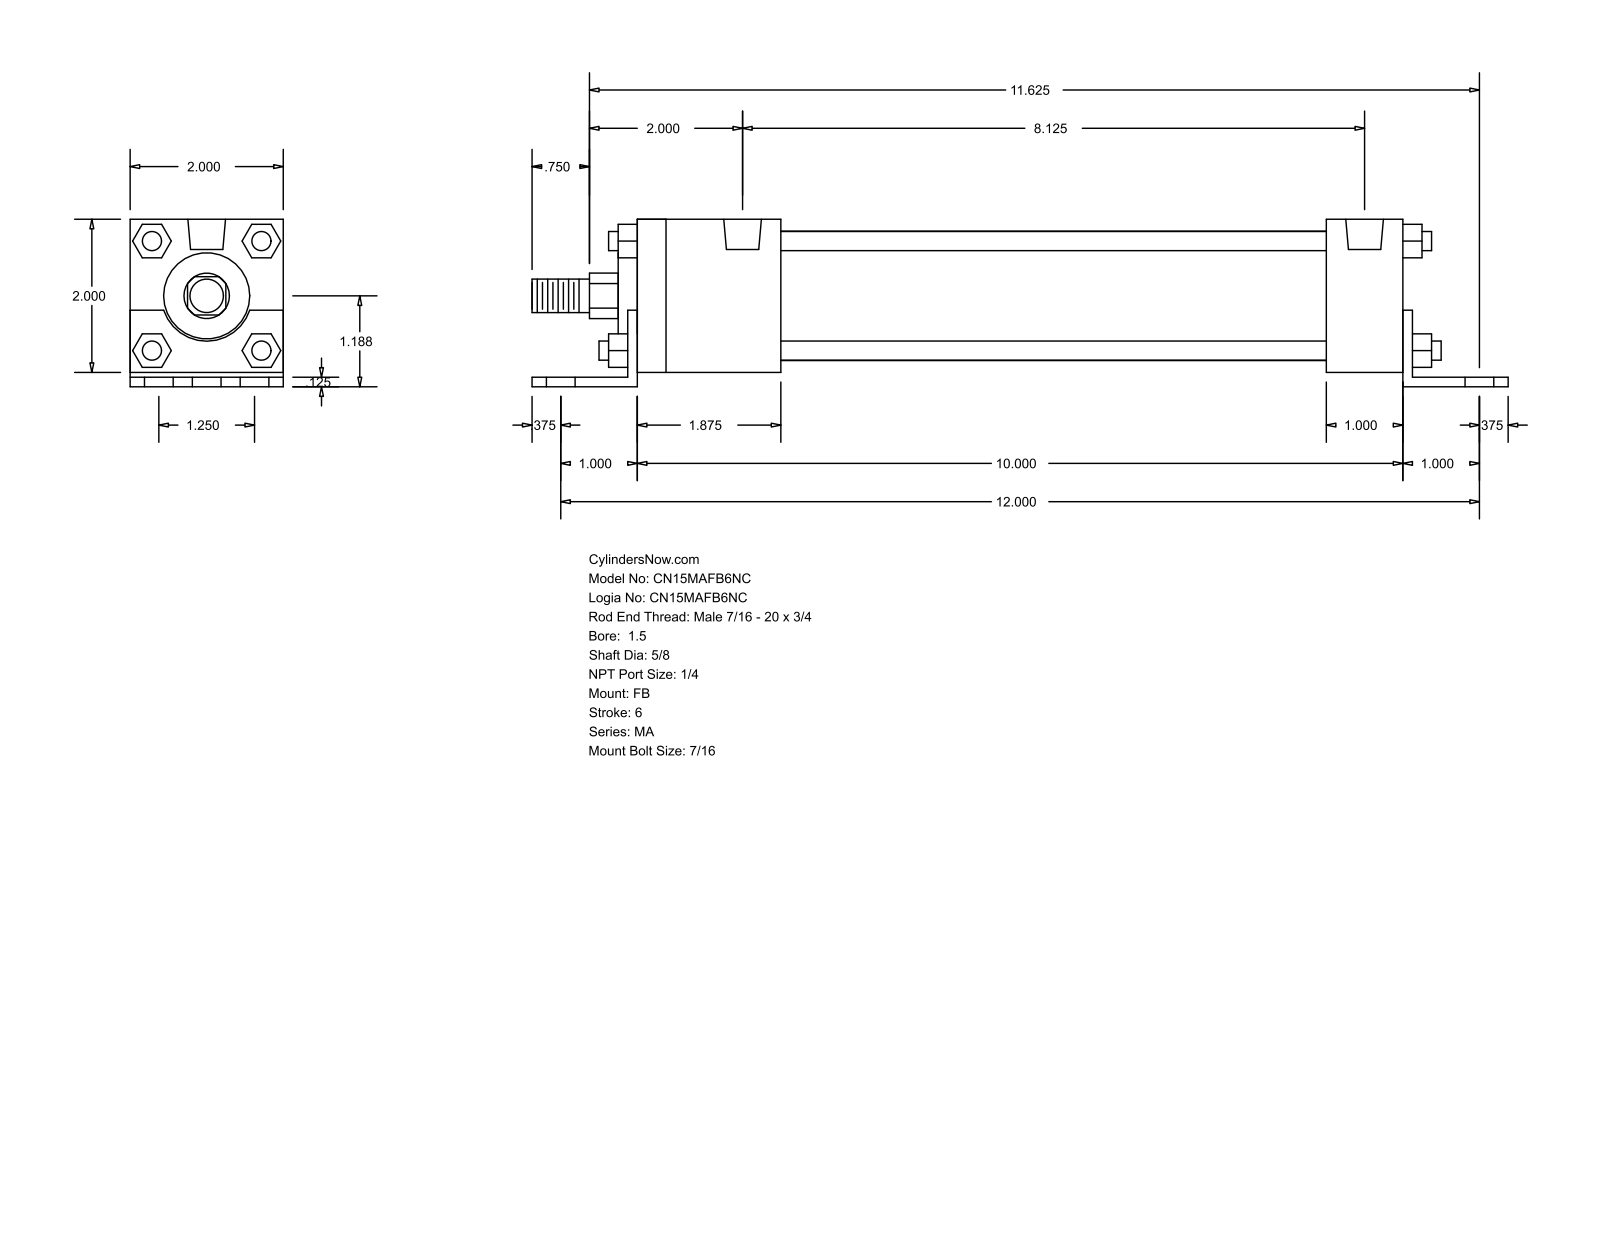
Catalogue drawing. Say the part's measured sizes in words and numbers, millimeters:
The part is named "MA_FB__0150_0.625". Its 3-D file was written by "GSSL Pune (CONFIG_CONTROL_DESIGN)". It is 0 solids with 140 faces: 105 planar, 35 cylindrical and 0 other. Overall it measures 323.85 by 55.56 by 50.8 millimeters. Round holes: 6 of diameter 11.11, 4 of diameter 7.94, 2 of diameter 12.49. Round bosses or shafts: 4 of diameter 6.35, 1 of diameter 42.93, 1 of diameter 28.57, 1 of diameter 15.88, 1 of diameter 11.11. Partial cylindrical surfaces (rounded edges, fillets, slot ends): 1 of radius 7.54, 1 of radius 15.05. The main face-to-face distances are 50.8, 3.17, 4.76, 55.56, 1.59, 52.39, 260.35, 6.35, 3.18, 28.58. The hole center spacings are 15.88, 305.21, 304.8, 31.76, 41.27, 62.38, 206.38, 244.99.
